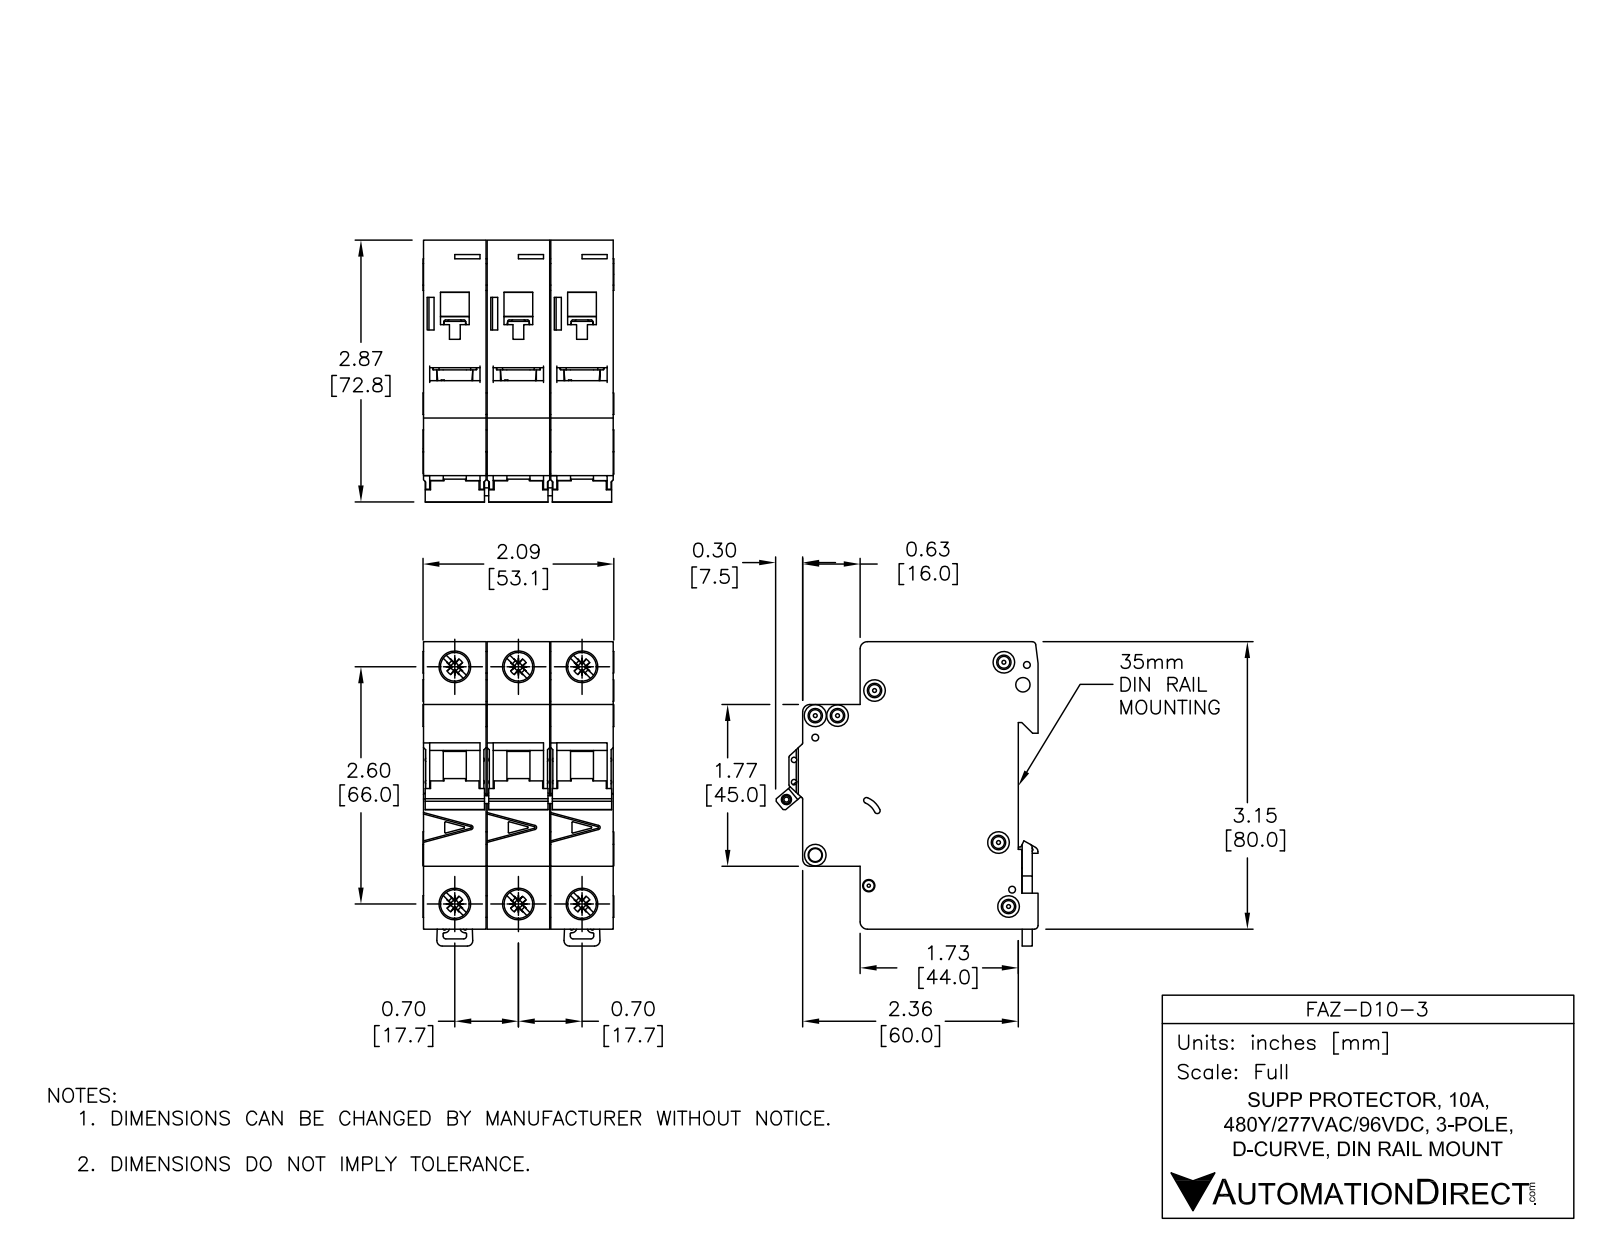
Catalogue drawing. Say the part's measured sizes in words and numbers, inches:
The part is named "FAZ-D10-3". Its 3-D file was written by "SolidWorks 2014 (AUTOMOTIVE_DESIGN)". It is 11 solids with 1650 faces: 697 planar, 590 cylindrical and 363 other. Overall it measures 3.338 by 2.876 by 2.091 inches. Its volume is 13.71 cubic inches and its surface area 89.98 square inches. Round holes: 6 of diameter 0.142, 4 of diameter 0.323, 3 of diameter 0.075, 2 of diameter 0.043, 2 of diameter 0.059, 2 of diameter 0.157, 2 of diameter 0.281, 1 of diameter 0.085, 1 of diameter 0.087, 1 of diameter 0.1, 1 of diameter 0.13, 1 of diameter 0.134. Round bosses or shafts: 4 of diameter 0.236, 3 of diameter 0.098, 2 of diameter 0.323. Partial cylindrical surfaces (rounded edges, fillets, slot ends): 68 of radius 0.01, 25 of radius 0.02, 12 of radius 0.039, 12 of radius 0.079, 11 of radius 0.008, 3 of radius 0.071, 2 of radius 0.031, 2 of radius 0.118. The main face-to-face distances are 0.697, 0.689, 1.394, 1.386, 2.083, 0.705, 3.129, 0.217, 1.949, 1.732. The hole center spacings are 0.697, 2.69, 2.598, 0.244, 0.537, 1.394, 2.948, 0.189.
